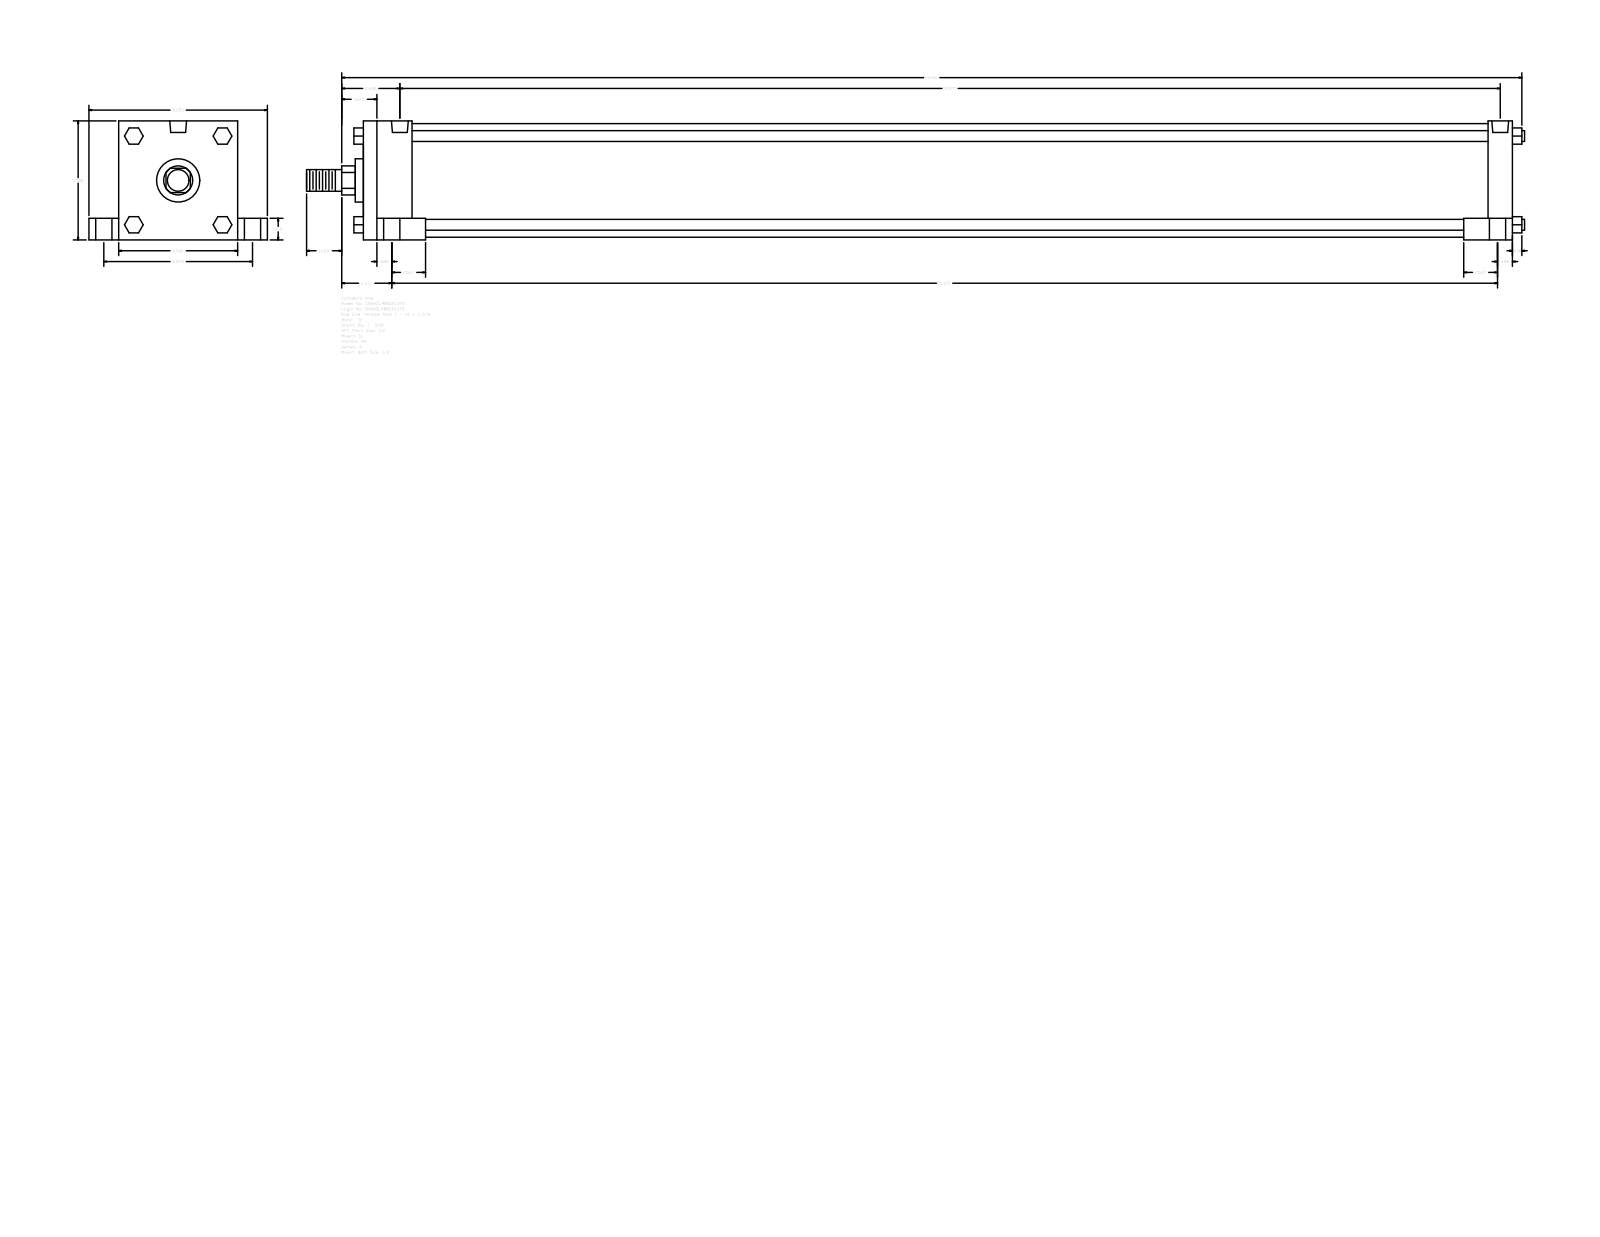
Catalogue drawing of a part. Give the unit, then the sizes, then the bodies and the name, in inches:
Units: inches
Overall size (bounding box): 56.313 × 8.25 × 5.5
Round holes (diameter × count): ⌀0.344 ×4, ⌀0.75 ×4, ⌀1 ×4, ⌀0.778 ×2
Round bosses / shafts (diameter × count): ⌀0.5 ×4, ⌀5.25 ×1, ⌀2 ×1, ⌀1.375 ×1, ⌀1 ×1
Partial cylindrical surfaces — rounded edges, fillets, slot ends (radius × count): R0.672 ×1
Main face-to-face distances: 5.5, 53.125, 2.25, 1.125, 1, 4.5, 1.375, 6.875, 52, 49.75
Hole centre spacings: 0.094, 3.437, 3.44, 3.458, 3.469, 6.875, 50.687, 50.772
Bodies: 0 solids, 150 faces (114 planar, 36 cylindrical, 0 other)
Part name (STEP PRODUCT): A_SL__0500_1.375
STEP written by: GSSL Pune (CONFIG_CONTROL_DESIGN)
